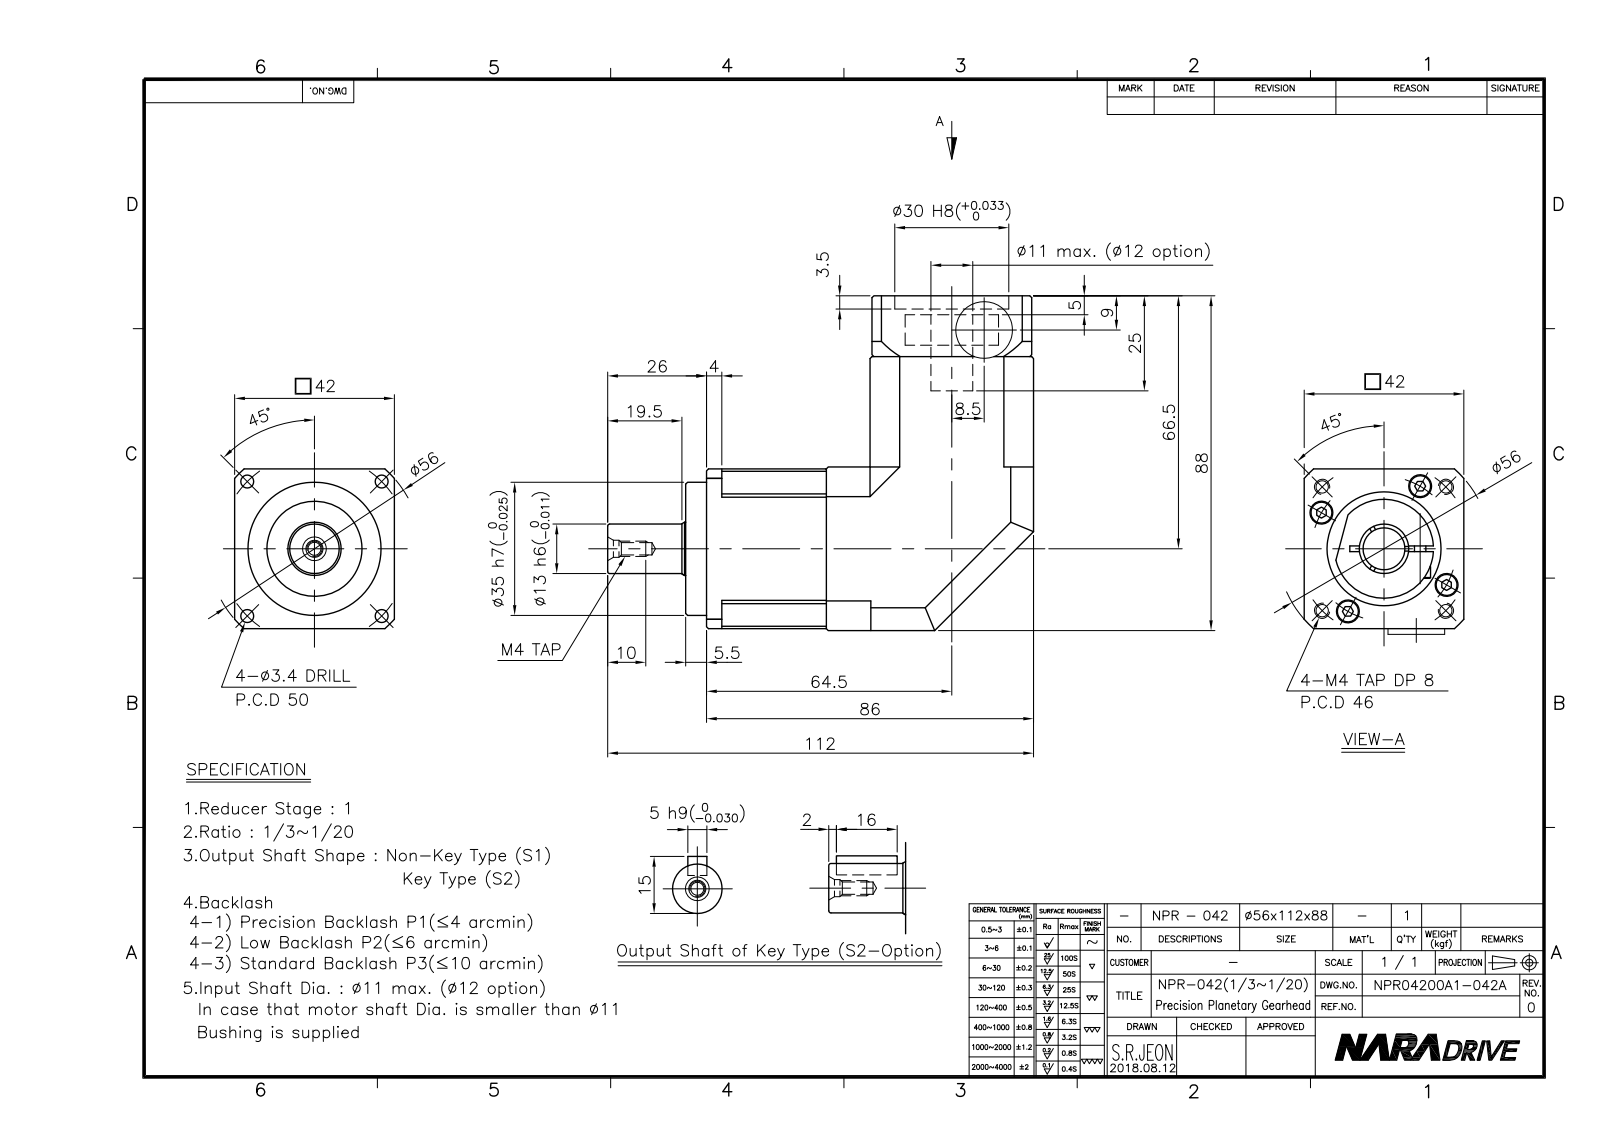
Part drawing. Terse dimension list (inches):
name: NP04200A1-042A-S1
written by: Autodesk Inventor 2015 (AUTOMOTIVE_DESIGN)
unit: in
bodies: 2 solids, 407 faces (203 planar, 104 cylindrical, 100 other)
size: 4.409 × 3.465 × 1.732
volume: 11.79 in³; area: 61.43 in²
holes: 13× ⌀0.134, 9× ⌀0.097, 8× ⌀0.236, 5× ⌀0.128, 2× ⌀1.181, 1× ⌀0.177, 1× ⌀0.276, 1× ⌀0.335, 1× ⌀0.433, 1× ⌀0.512, 1× ⌀1.102, 1× ⌀1.26
bosses: 9× ⌀0.217, 9× ⌀0.118, 1× ⌀1.378, 1× ⌀1.024, 1× ⌀0.984, 1× ⌀0.591, 1× ⌀0.551, 1× ⌀0.512
rounds: 4× R0.197, 2× R1.004, 2× R1.102, 1× R0.118, 1× R0.984
face distances: 0.02, 1.673, 1.693, 1.654, 1.988, 0.315, 0.846, 0.217, 2.618, 0.295
hole spacings: 0.263, 1.129, 1.413, 1.789, 0.817, 1.155, 0.748, 1.281
